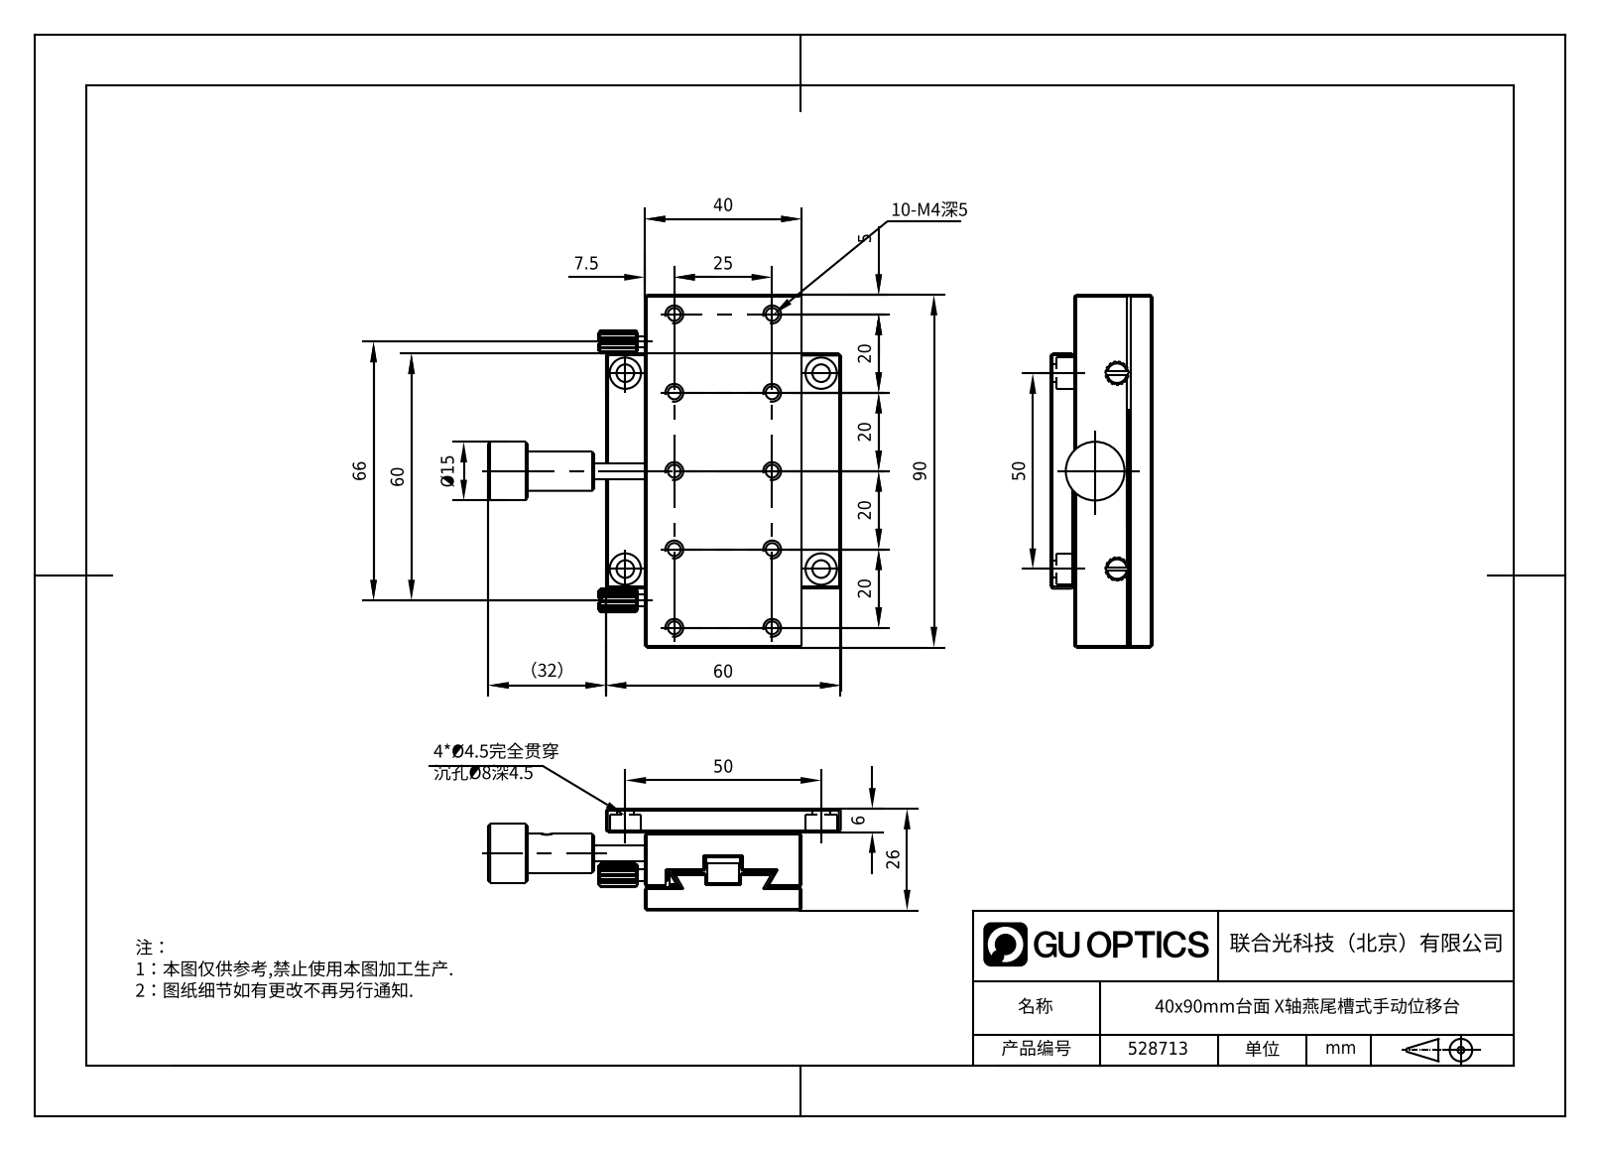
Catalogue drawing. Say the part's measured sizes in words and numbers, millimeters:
The part is named "528713". Its 3-D file was written by "SolidWorks 2020 (CONFIG_CONTROL_DESIGN)". It is 12 solids with 810 faces: 459 planar, 181 cylindrical and 170 other. Overall it measures 90 by 82.9 by 26 millimeters. Its volume is 91 078 cubic millimeters and its surface area 43 820 square millimeters. Round holes: 14 of diameter 3.3, 12 of diameter 2.5, 11 of diameter 4.5, 11 of diameter 8, 3 of diameter 2.05, 2 of diameter 2.8, 1 of diameter 2.9, 1 of diameter 4, 1 of diameter 4.1, 1 of diameter 5. Round bosses or shafts: 2 of diameter 10, 2 of diameter 9, 2 of diameter 7, 2 of diameter 2.95, 1 of diameter 8, 1 of diameter 7.4, 1 of diameter 6.85, 1 of diameter 3. Partial cylindrical surfaces (rounded edges, fillets, slot ends): 1 of radius 10. The main face-to-face distances are 6, 20, 14, 10, 5.5, 19.5, 25.5, 16, 26, 3.8. The hole center spacings are 27.95, 15.21, 20, 31.32, 32.02, 41.23, 45.07, 25.
